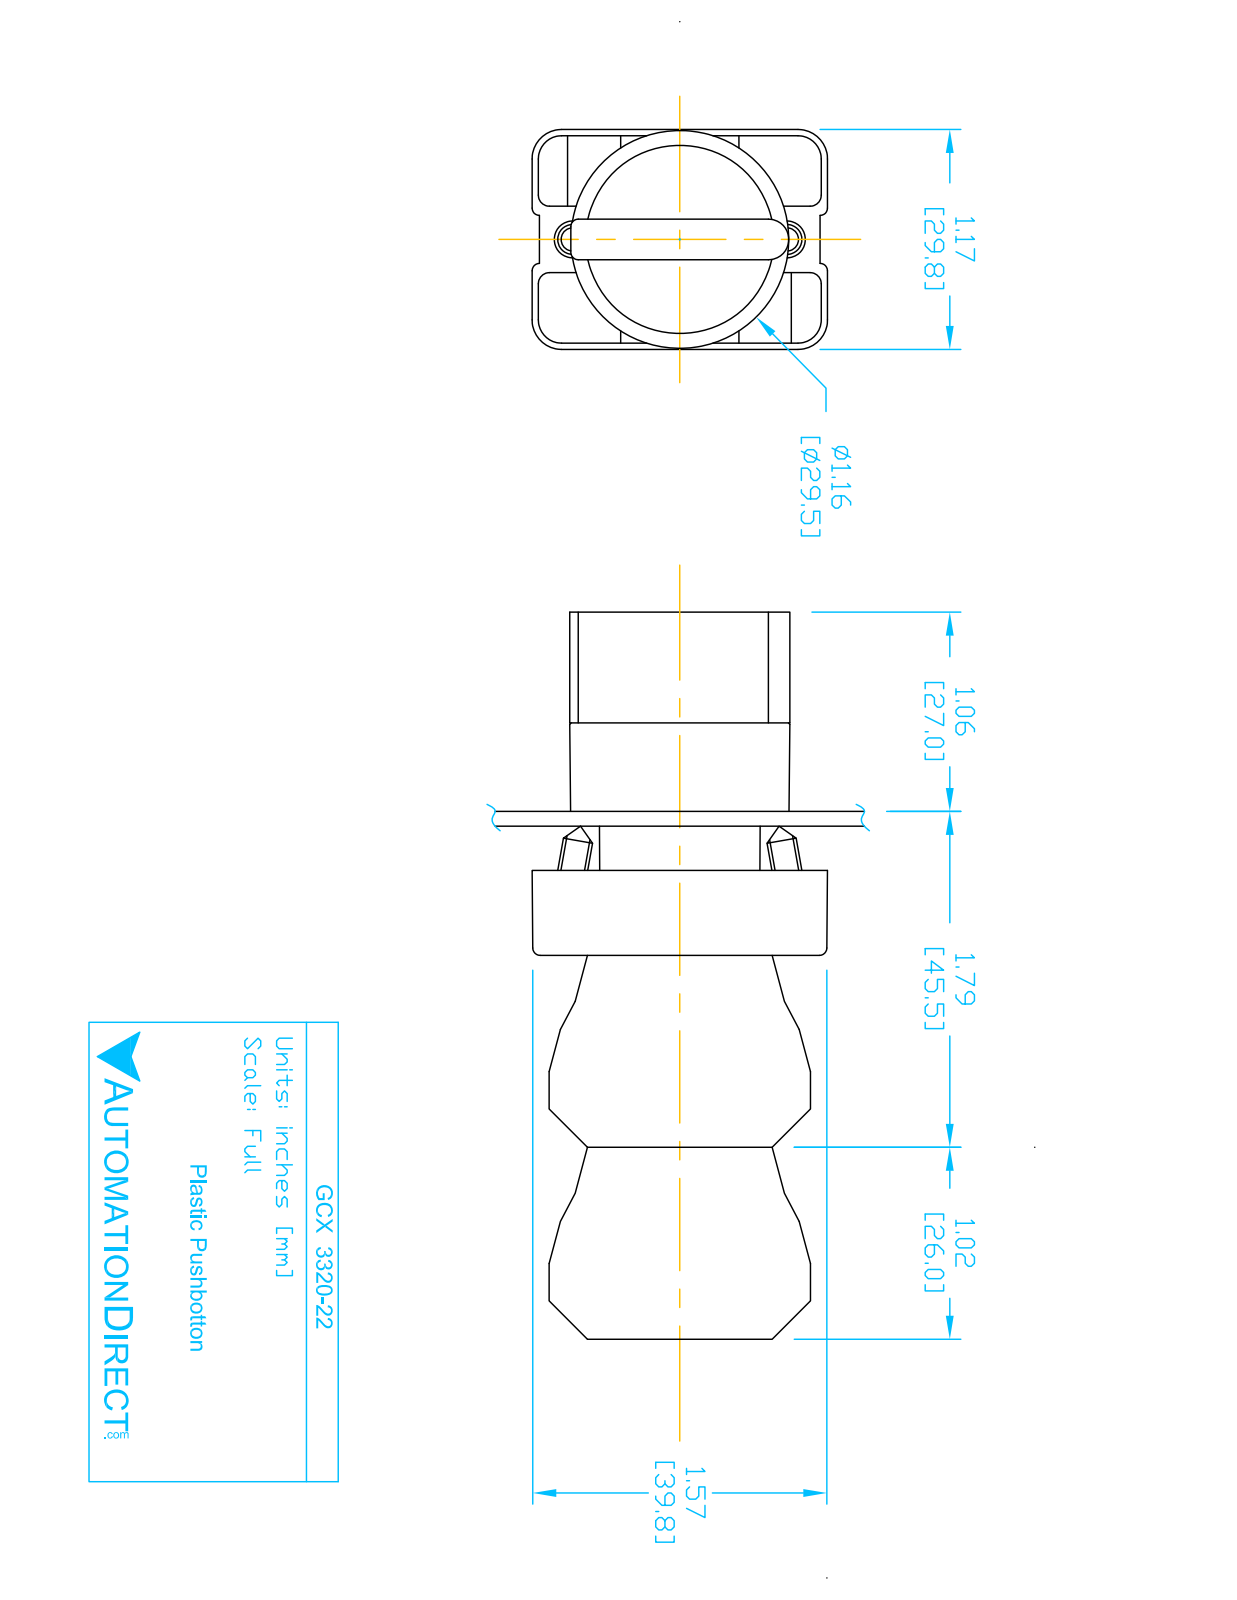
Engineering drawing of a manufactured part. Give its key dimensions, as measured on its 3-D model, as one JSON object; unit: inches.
{"part_name": "GCX3320-22; ECX3029-2; ecx1030; ecx1040 (+1 more)", "step_written_by": "SolidWorks 2016 (AUTOMOTIVE_DESIGN)", "units": "inches", "bodies": {"solids": 9, "faces": 675, "planar": 457, "cylindrical": 179, "other": 39}, "overall_size": [3.803, 1.581, 1.177], "volume_in3": 3.832, "surface_area_in2": 48.86, "round_holes": [[0.079, 4], [0.087, 2], [0.124, 2], [0.13, 2], [0.197, 1], [0.878, 1], [0.888, 1], [1.024, 1]], "round_bosses_or_shafts": [[0.157, 2], [1.175, 1], [1.004, 1], [0.945, 1], [0.856, 1], [0.78, 1]], "partial_cylinders_radius": [[0.059, 24], [0.041, 12], [0.124, 12], [0.157, 12], [0.039, 6], [0.02, 2], [0.063, 2], [0.079, 2]], "face_to_face_distances": [0.598, 0.579, 1.024, 1.177, 0.02, 1.744, 0.72, 0.124, 2.768, 0.474], "hole_center_spacings": [0.236, 0.544, 1.008, 0.98, 0.472, 0.49, 1.088]}
